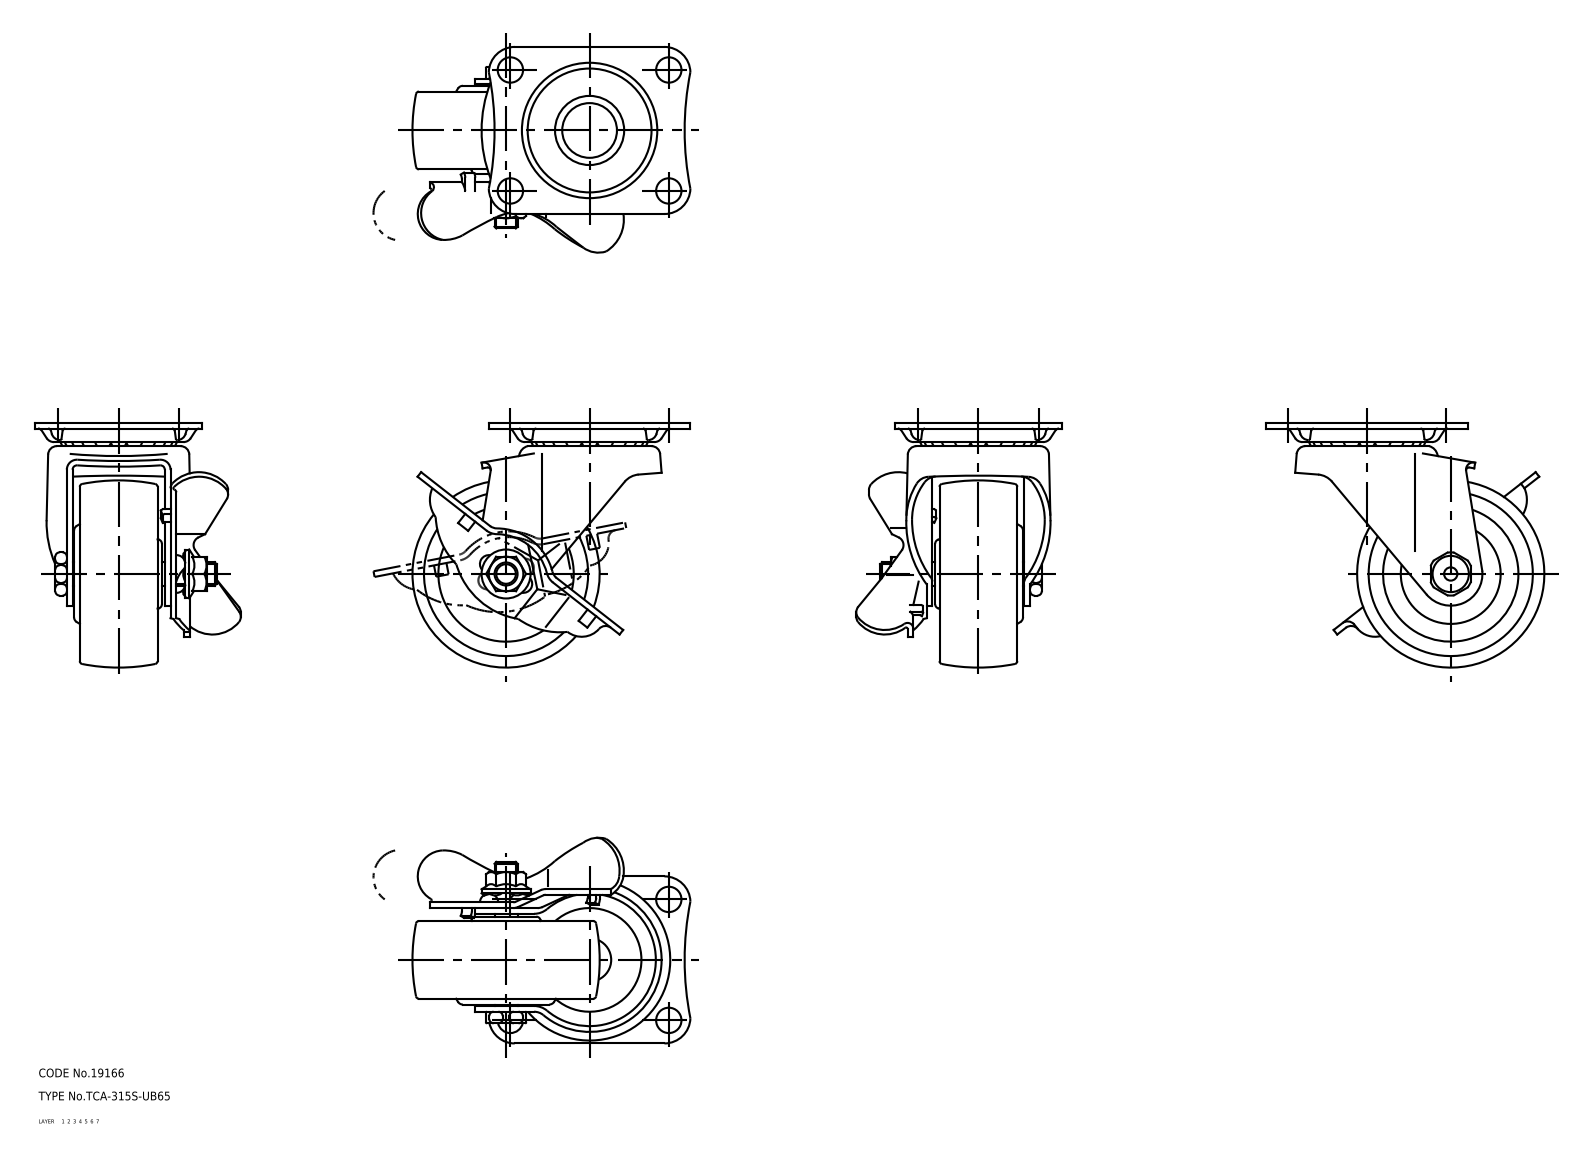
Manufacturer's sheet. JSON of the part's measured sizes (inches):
{"part_name": "wheel; mounting plate; main shaft; lever (+2 more)", "step_written_by": "CADfix (AUTOMOTIVE_DESIGN)", "units": "inches", "bodies": {"solids": 6, "faces": 529, "planar": 0, "cylindrical": 0, "other": 529}, "overall_size": [3.799, 3.346, 2.811], "volume_in3": 6.901, "surface_area_in2": 77.54}
